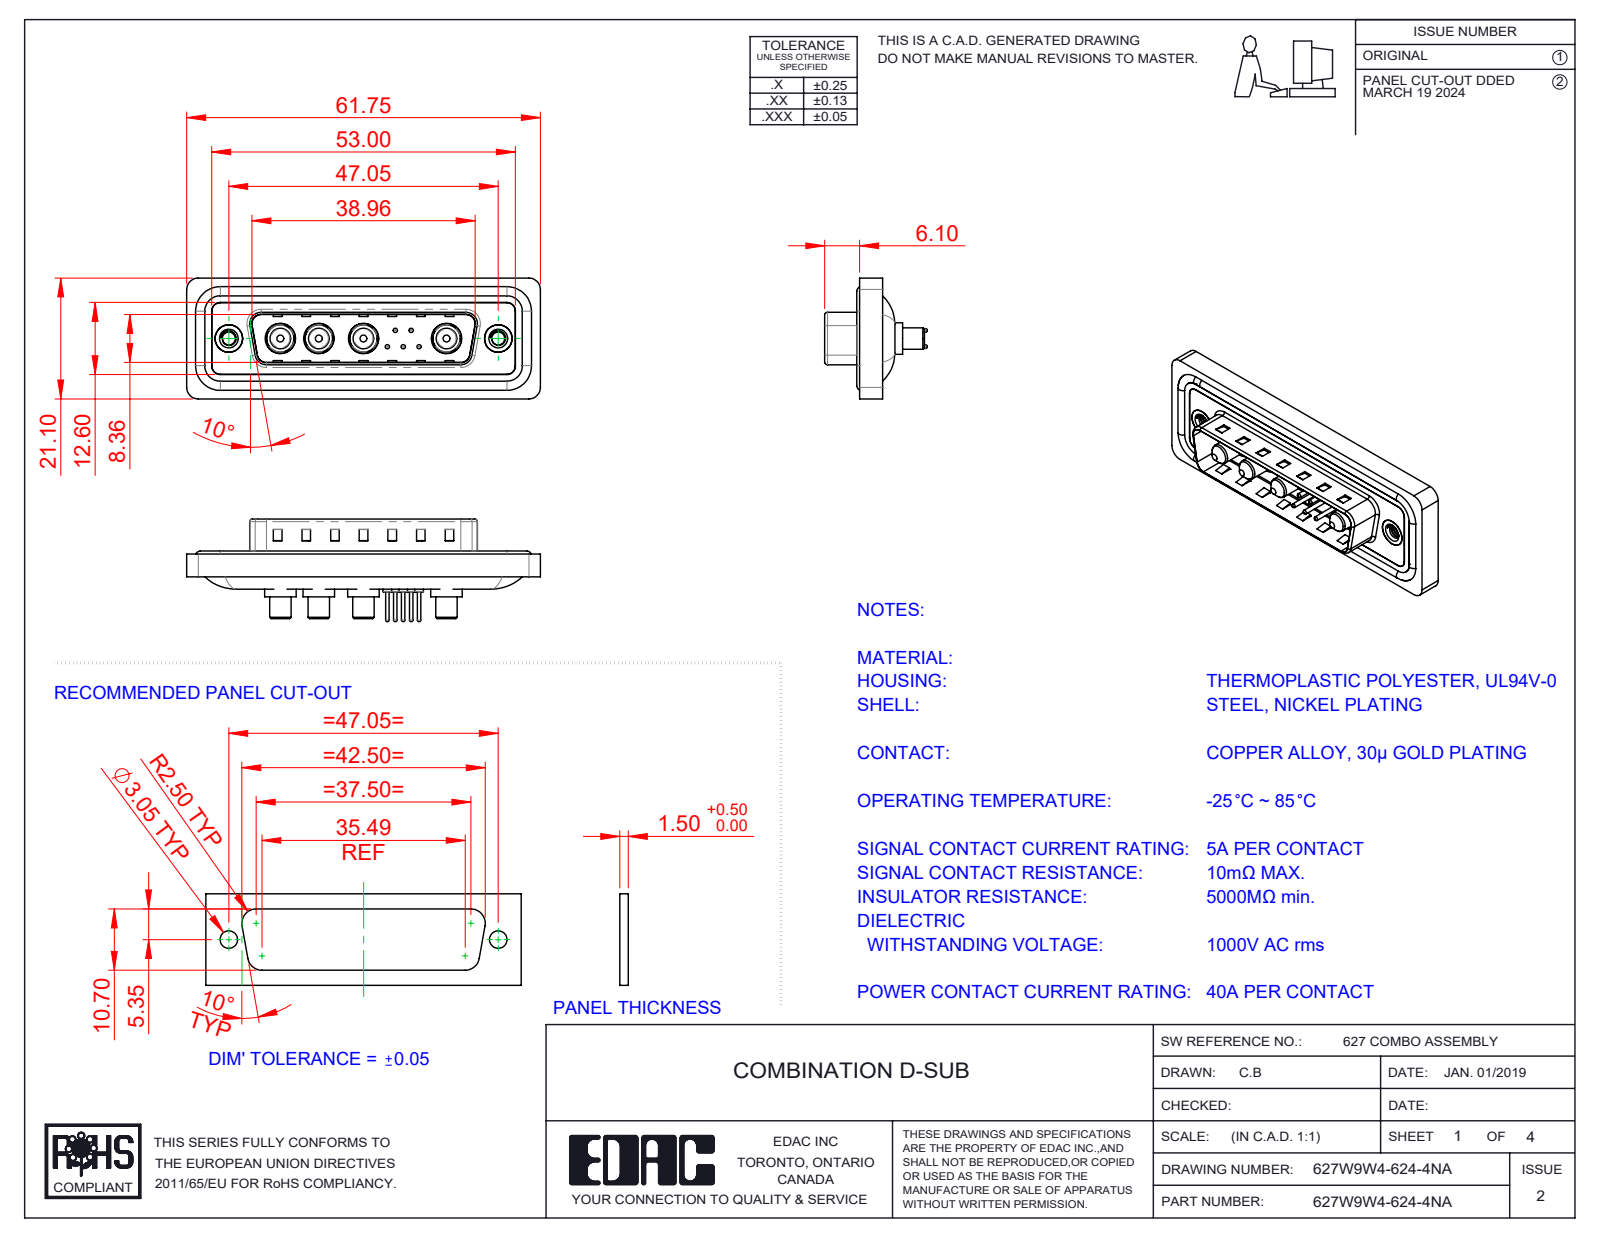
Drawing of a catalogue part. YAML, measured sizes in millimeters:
part_name: "627Combo Shell Front_25 Contacts; 627Combo Shell Rear_25 Contacts; Power Pin_40A S; 627Combo Contact Row 2_24 (+5 more)"
step_written_by: "SolidWorks 2023 (CONFIG_CONTROL_DESIGN)"
units: millimeters
bodies: {solids: 20, faces: 822, planar: 284, cylindrical: 336, other: 202}
overall_size: [61.75, 21.1, 17.9]
volume: 7480
surface_area: 11877
round_holes:
  - {diameter: 0.75, count: 5}
  - {diameter: 1.6, count: 5}
  - {diameter: 2, count: 5}
  - {diameter: 4.85, count: 4}
  - {diameter: 5.3, count: 4}
  - {diameter: 2.26, count: 2}
  - {diameter: 4, count: 2}
  - {diameter: 4.8, count: 2}
  - {diameter: 5, count: 2}
round_bosses_or_shafts:
  - {diameter: 1.5, count: 5}
  - {diameter: 0.6, count: 5}
  - {diameter: 5.5, count: 4}
  - {diameter: 5.2, count: 4}
  - {diameter: 4.75, count: 4}
  - {diameter: 3.75, count: 4}
  - {diameter: 3.6, count: 4}
  - {diameter: 1.6, count: 4}
partial_cylinders:
  - {radius: 1.5, count: 22}
  - {radius: 2, count: 18}
  - {radius: 0.5, count: 8}
  - {radius: 1.6, count: 8}
  - {radius: 0.25, count: 4}
  - {radius: 0.6, count: 4}
  - {radius: 0.65, count: 4}
  - {radius: 0.9, count: 4}
face_to_face_distances: [0.4, 1.5, 1.1, 0.5, 1.6, 3.1, 2.9, 0.82, 9.58, 5.65]
hole_center_spacings: [3.16, 2.77, 5.04, 14.51, 2.78, 4.4, 4.41, 5]
